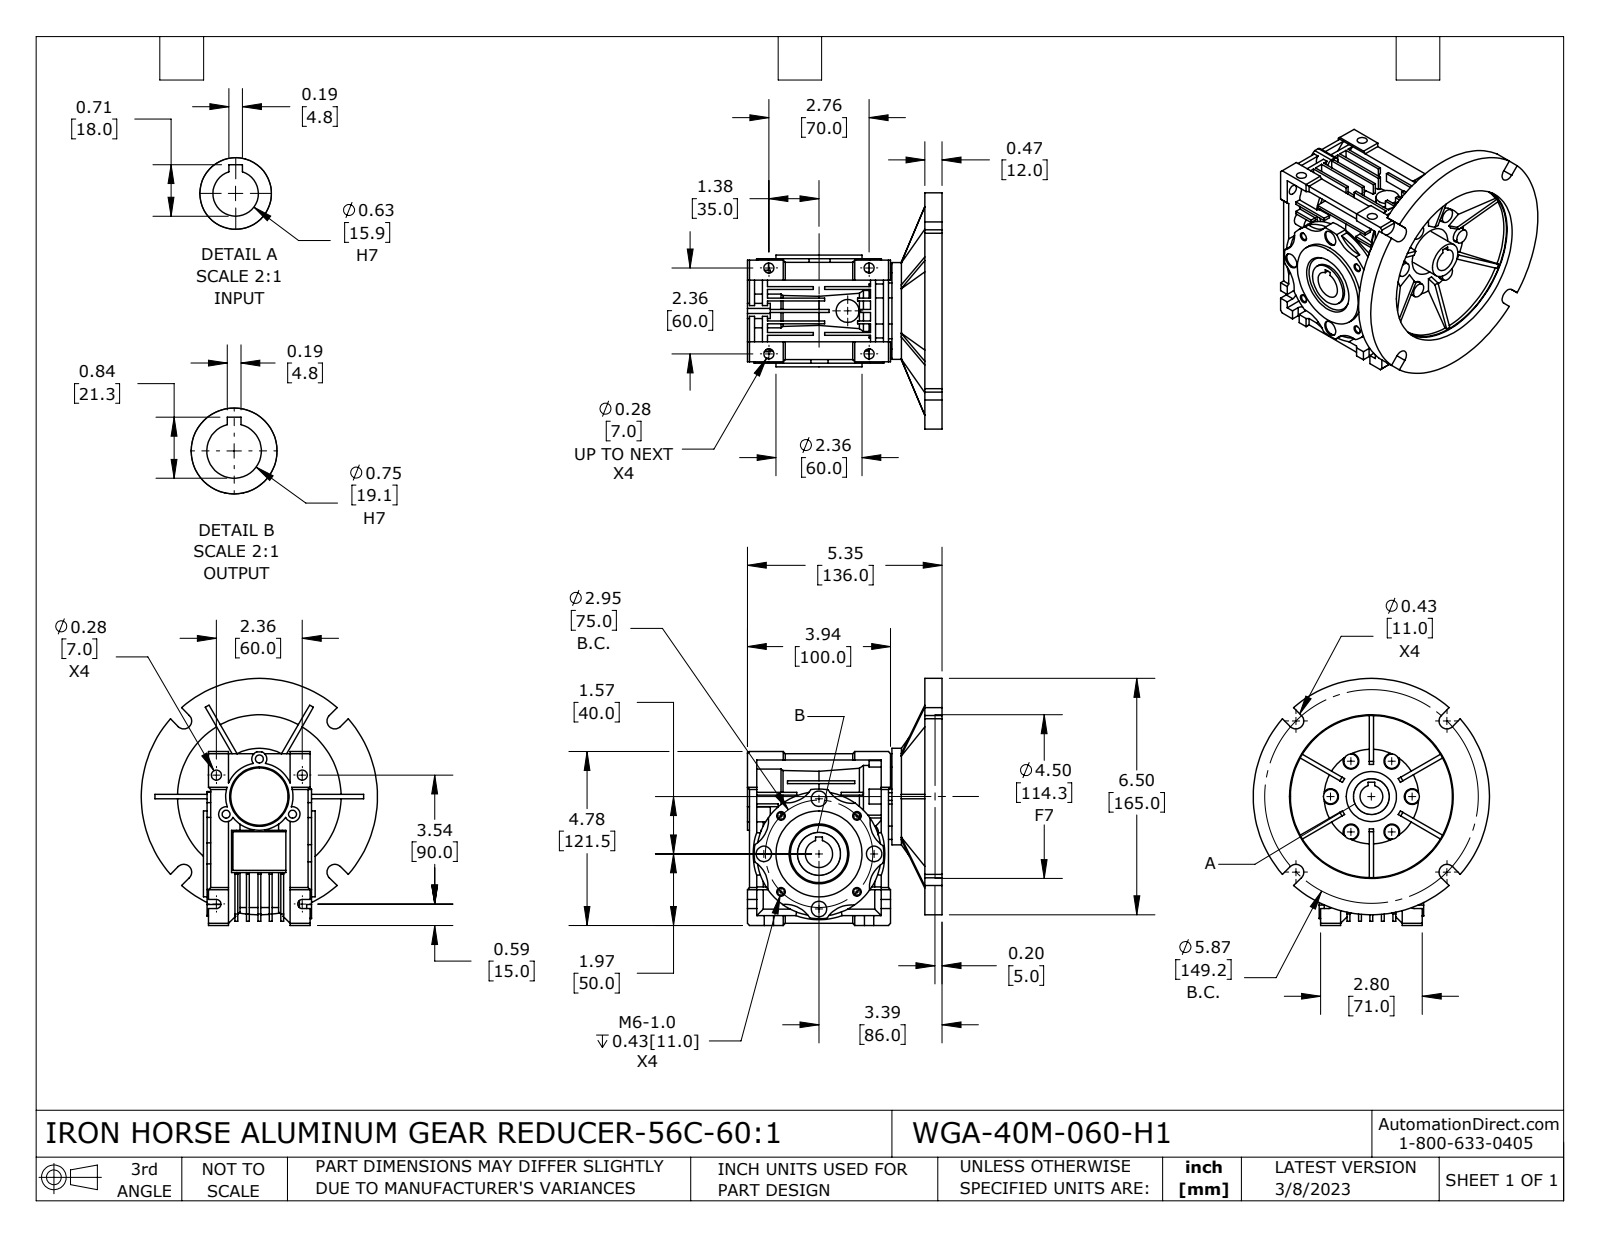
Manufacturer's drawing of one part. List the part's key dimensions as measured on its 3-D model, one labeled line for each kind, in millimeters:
Part name (STEP PRODUCT): WGA-40M-060-H1
STEP written by: SolidWorks 2021 (CONFIG_CONTROL_DESIGN)
Units: millimetres
Bodies: 4 solids, 856 faces (511 planar, 251 cylindrical, 94 other)
Overall size (bounding box): 172.5 × 165 × 136
Volume: 824 900 mm³ · Surface area: 203 200 mm²
Round holes (diameter × count): ⌀7 ×6, ⌀11 ×6, ⌀4.9 ×4, ⌀10.8 ×4, ⌀5.6 ×3, ⌀15.9 ×1, ⌀16.5 ×1, ⌀19.1 ×1, ⌀23 ×1, ⌀28 ×1, ⌀30 ×1, ⌀35 ×1
Round bosses / shafts (diameter × count): ⌀10 ×6, ⌀165 ×1, ⌀75 ×1, ⌀67.5 ×1, ⌀60 ×1, ⌀54 ×1, ⌀47 ×1, ⌀36 ×1
Partial cylindrical surfaces — rounded edges, fillets, slot ends (radius × count): R20 ×8, R3.2 ×6, R5.2 ×6, R5.5 ×4, R5.3 ×3, R43.5 ×1, R43.6 ×1, R45.2 ×1
Main face-to-face distances: 8, 12, 2, 24, 6, 1.5, 16, 2.5, 10, 5
Hole centre spacings: 28.5, 29.1, 70.2, 49.4, 37.5, 38.5, 53, 54.5
